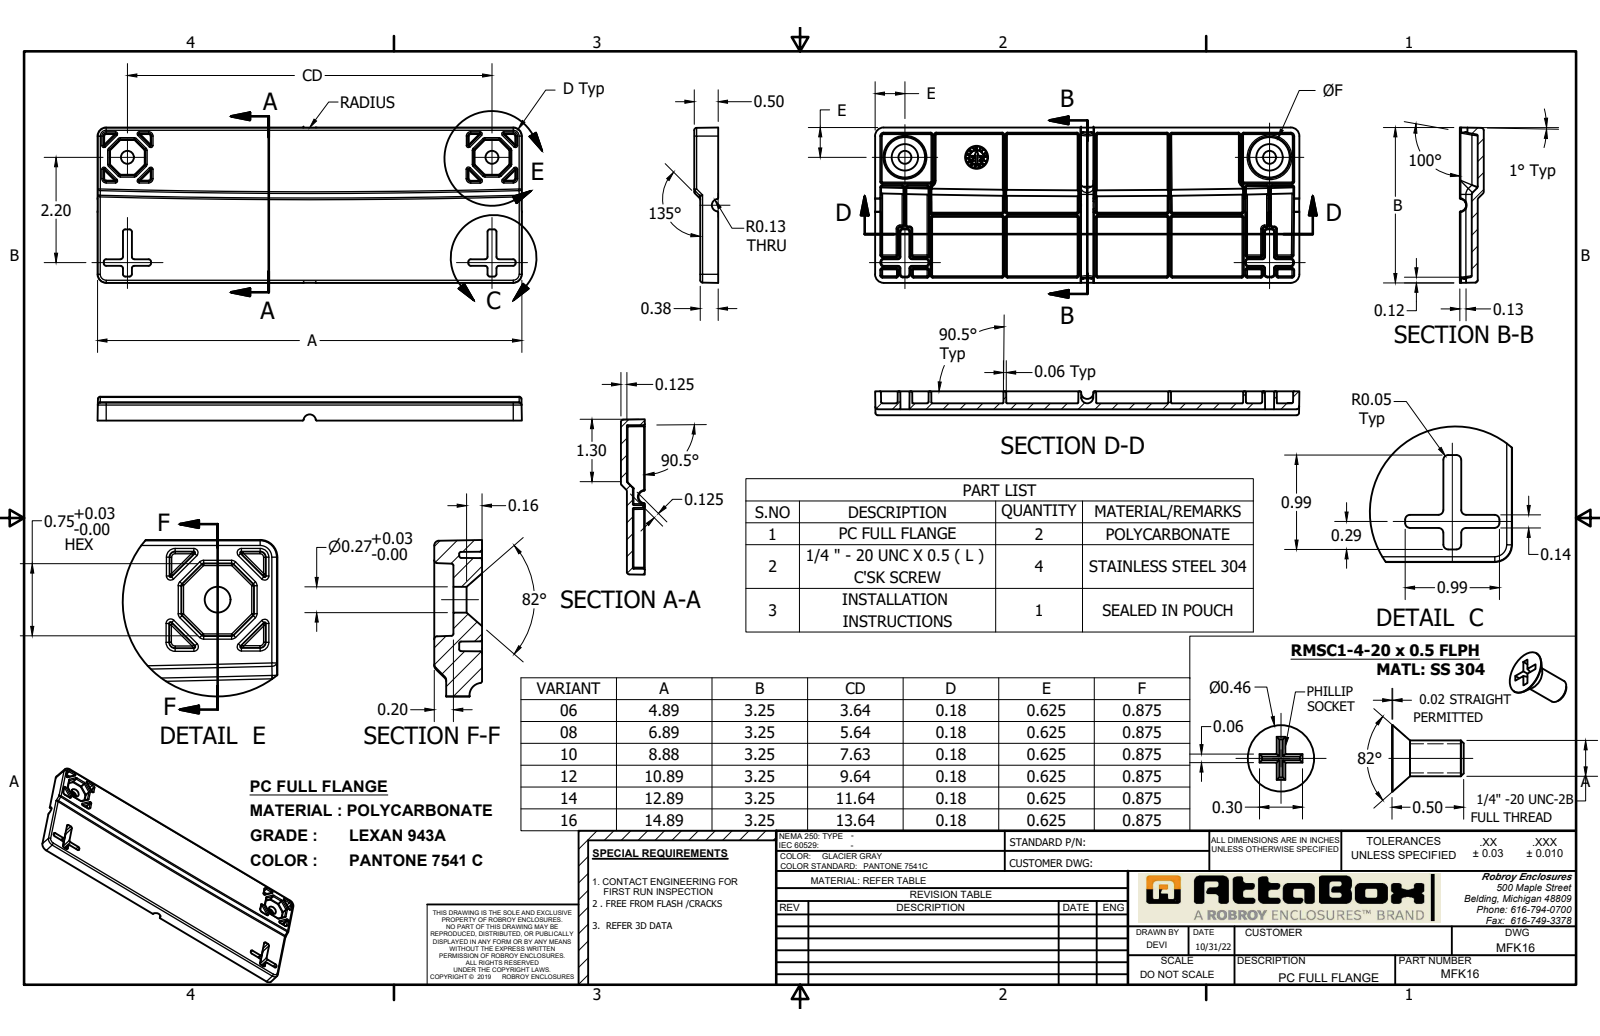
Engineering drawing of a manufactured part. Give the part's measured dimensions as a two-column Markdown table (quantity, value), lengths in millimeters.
| quantity | value |
| --- | --- |
| part name | MFK16_Default |
| STEP written by | SolidWorks 2023 (CONFIG_CONTROL_DESIGN) |
| units | millimeters |
| bodies | 1 solid, 1195 faces (334 planar, 397 cylindrical, 464 other) |
| overall size | 378.2 × 82.6 × 12.7 |
| volume | 135 900 mm³ |
| surface area | 93 290 mm² |
| round holes (diameter × count) | 6.9 × 2 |
| partial cylindrical surfaces (radius × count) | 0.5 × 122, 0.8 × 117, 1.3 × 6, 3.2 × 3, 3 × 1, 3.3 × 1, 3.3 × 1, 3.3 × 1 |
| main face-to-face distances | 6.4, 3.2, 3.2, 12.7, 9.5, 33.8, 44, 78, 163.9, 86 |
| hole center spacings | 346.5 |
